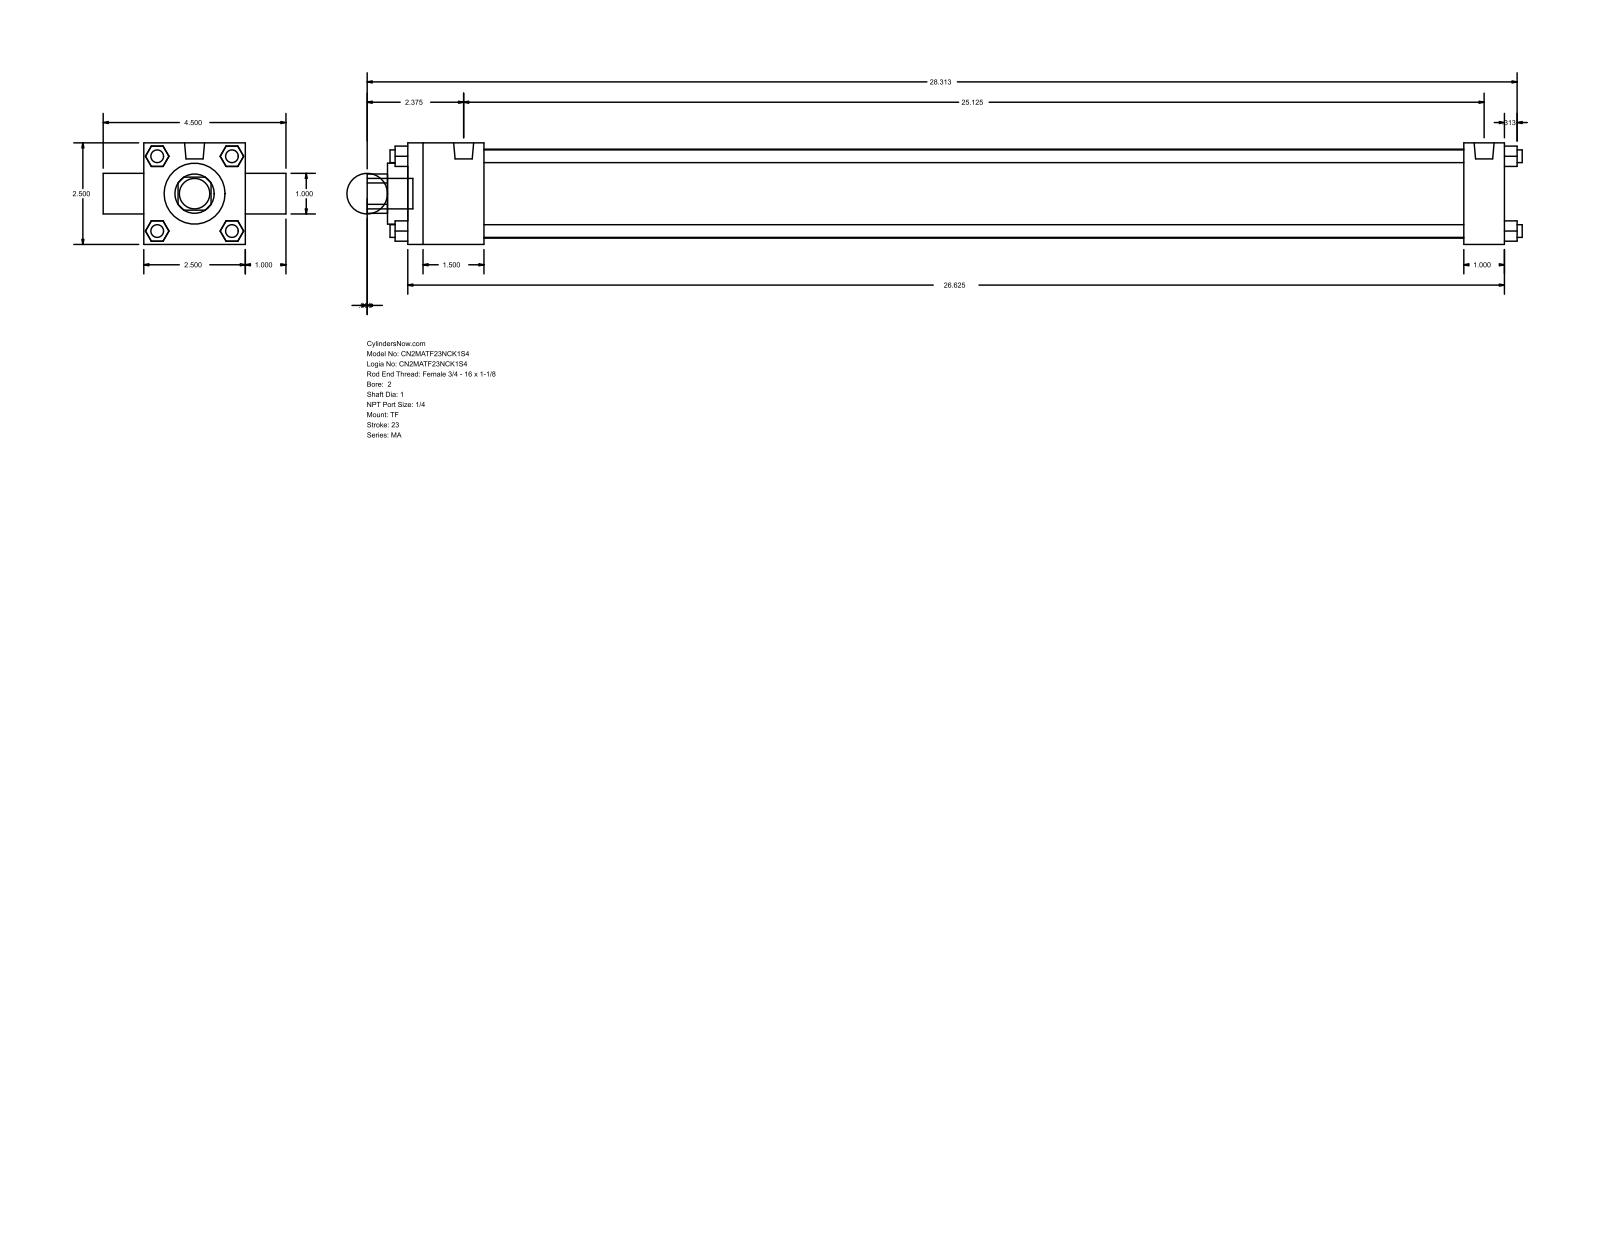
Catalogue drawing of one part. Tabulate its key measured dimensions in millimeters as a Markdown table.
| quantity | value |
| --- | --- |
| part name | MA_TF__0200_1 |
| STEP written by | GSSL Pune (CONFIG_CONTROL_DESIGN) |
| units | millimeters |
| bodies | 0 solids, 120 faces (92 planar, 28 cylindrical, 0 other) |
| overall size | 722.31 × 114.3 × 63.5 |
| round holes (diameter × count) | 25.4 × 2, 38.1 × 1, 55.63 × 1 |
| round bosses / shafts (diameter × count) | 7.94 × 7, 12.49 × 2, 19.05 × 1 |
| partial cylindrical surfaces (radius × count) | 12.29 × 1 |
| main face-to-face distances | 63.5, 25.4, 685.8, 12.7, 47.63, 660.4, 612.77, 638.17, 88.9, 23.37 |
